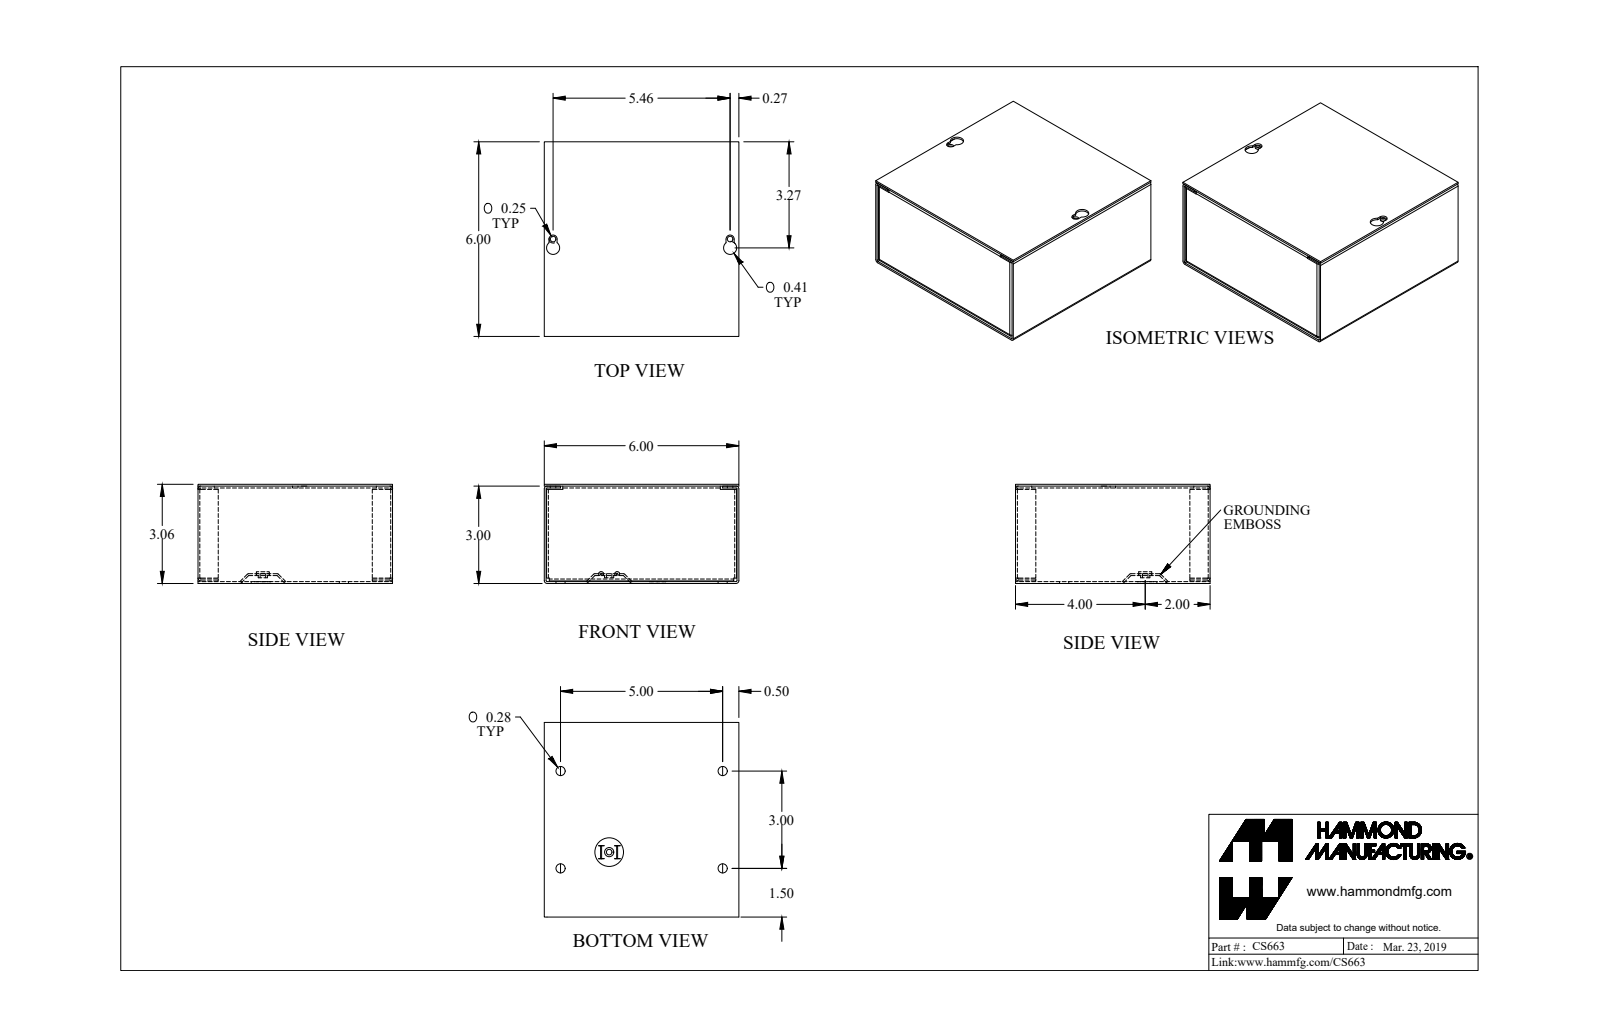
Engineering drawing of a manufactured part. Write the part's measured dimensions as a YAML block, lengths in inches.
part_name: "CS663_Default"
step_written_by: "SolidWorks 2019 (CONFIG_CONTROL_DESIGN)"
units: inches
bodies: {solids: 4, faces: 189, planar: 121, cylindrical: 60, other: 8}
overall_size: [6, 6, 3.057]
volume: 9.235
surface_area: 330.6
round_holes:
  - {diameter: 0.281, count: 4}
  - {diameter: 0.17, count: 3}
  - {diameter: 0.5, count: 1}
round_bosses_or_shafts:
  - {diameter: 0.492, count: 1}
  - {diameter: 0.284, count: 1}
partial_cylinders:
  - {radius: 0.029, count: 12}
  - {radius: 0.086, count: 12}
  - {radius: 0.057, count: 8}
  - {radius: 0.125, count: 2}
  - {radius: 0.203, count: 2}
face_to_face_distances: [0.057, 3, 5.943, 2.943, 6, 3.057, 5.886, 0.08, 2.863, 2.92]
hole_center_spacings: [1.517, 5.441, 3, 5, 5.831, 1.5, 1.581, 1.998]
